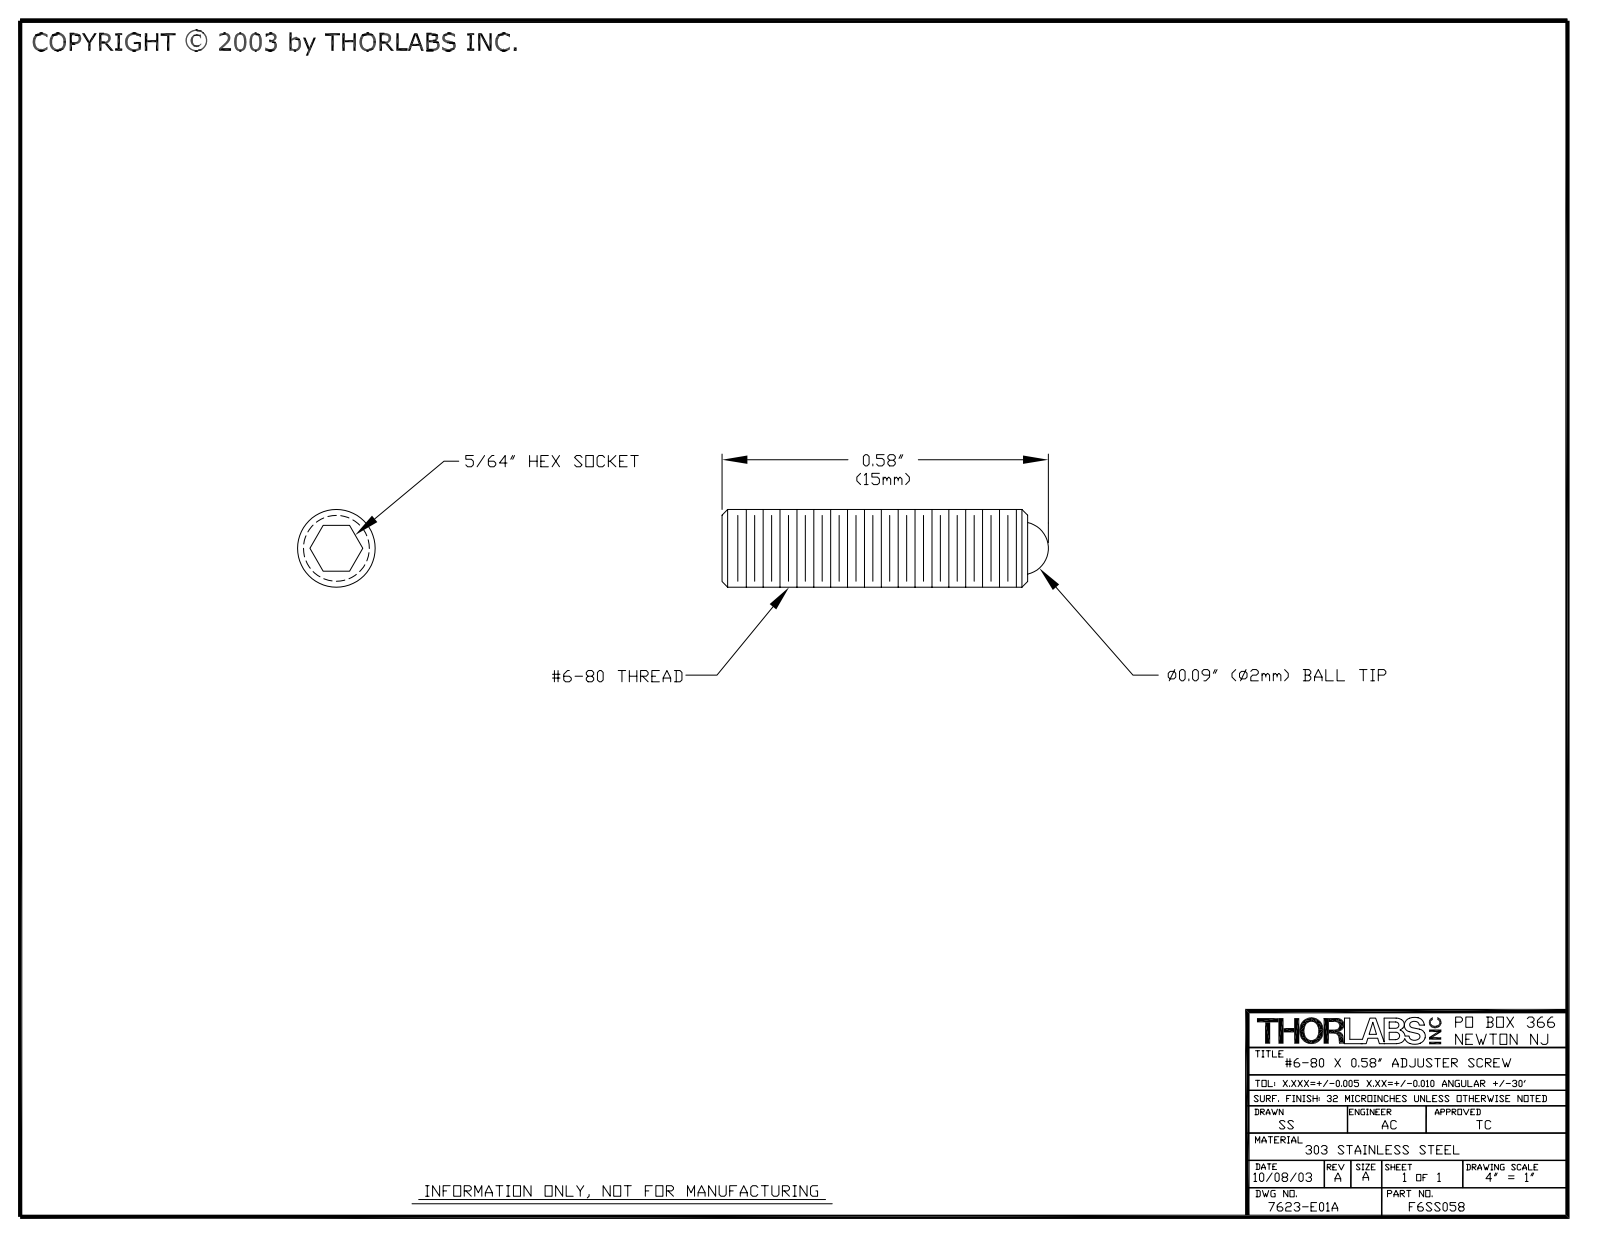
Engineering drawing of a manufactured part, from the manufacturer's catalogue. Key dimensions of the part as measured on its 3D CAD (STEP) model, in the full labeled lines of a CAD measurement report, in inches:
Part name (STEP PRODUCT): 7623-E0W
STEP written by: SolidWorks 2016 (AUTOMOTIVE_DESIGN)
Units: inches
Bodies: 2 solids, 30 faces (9 planar, 4 cylindrical, 17 other)
Overall size (bounding box): 0.58 × 0.138 × 0.138
Volume: 0.008 in³ · Surface area: 0.332 in²
Round holes (diameter × count): ⌀0.094 ×1
Round bosses / shafts (diameter × count): ⌀0.138 ×1
Main face-to-face distances: 0.078, 0.12, 0.543, 0.423
